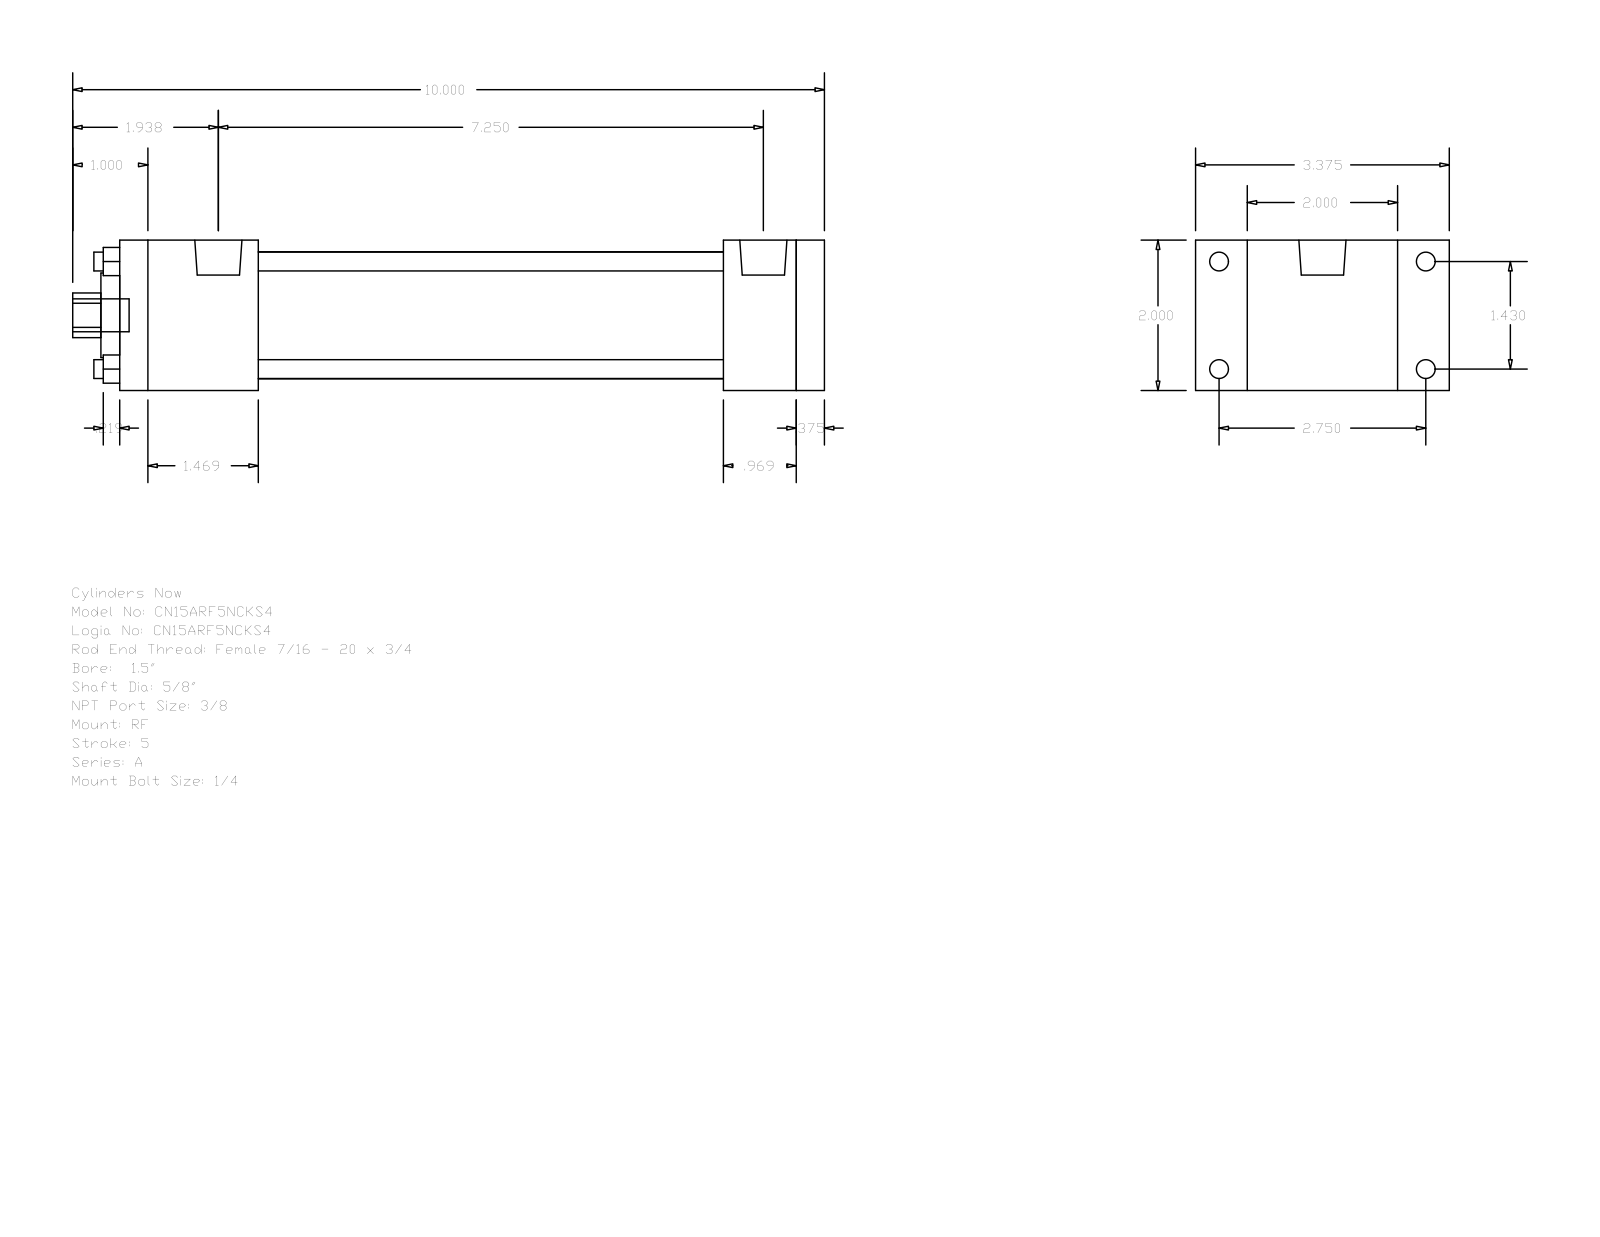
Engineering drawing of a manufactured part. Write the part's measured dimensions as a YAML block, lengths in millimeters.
part_name: "A_RF__0150_0.625"
step_written_by: "GSSL Pune (CONFIG_CONTROL_DESIGN)"
units: millimeters
bodies: {solids: 0, faces: 92, planar: 64, cylindrical: 28, other: 0}
overall_size: [254, 85.72, 50.8]
round_holes:
  - {diameter: 6.35, count: 4}
  - {diameter: 15.88, count: 1}
  - {diameter: 28.57, count: 1}
  - {diameter: 42.93, count: 1}
round_bosses_or_shafts:
  - {diameter: 6.35, count: 4}
  - {diameter: 5.56, count: 4}
  - {diameter: 15.93, count: 2}
  - {diameter: 11.11, count: 1}
partial_cylinders:
  - {radius: 7.54, count: 1}
face_to_face_distances: [50.8, 9.53, 238.12, 228.59, 203.99, 24.6, 34.13, 46.83, 157.16, 181.76]
hole_center_spacings: [25.68, 36.32, 51.36]
